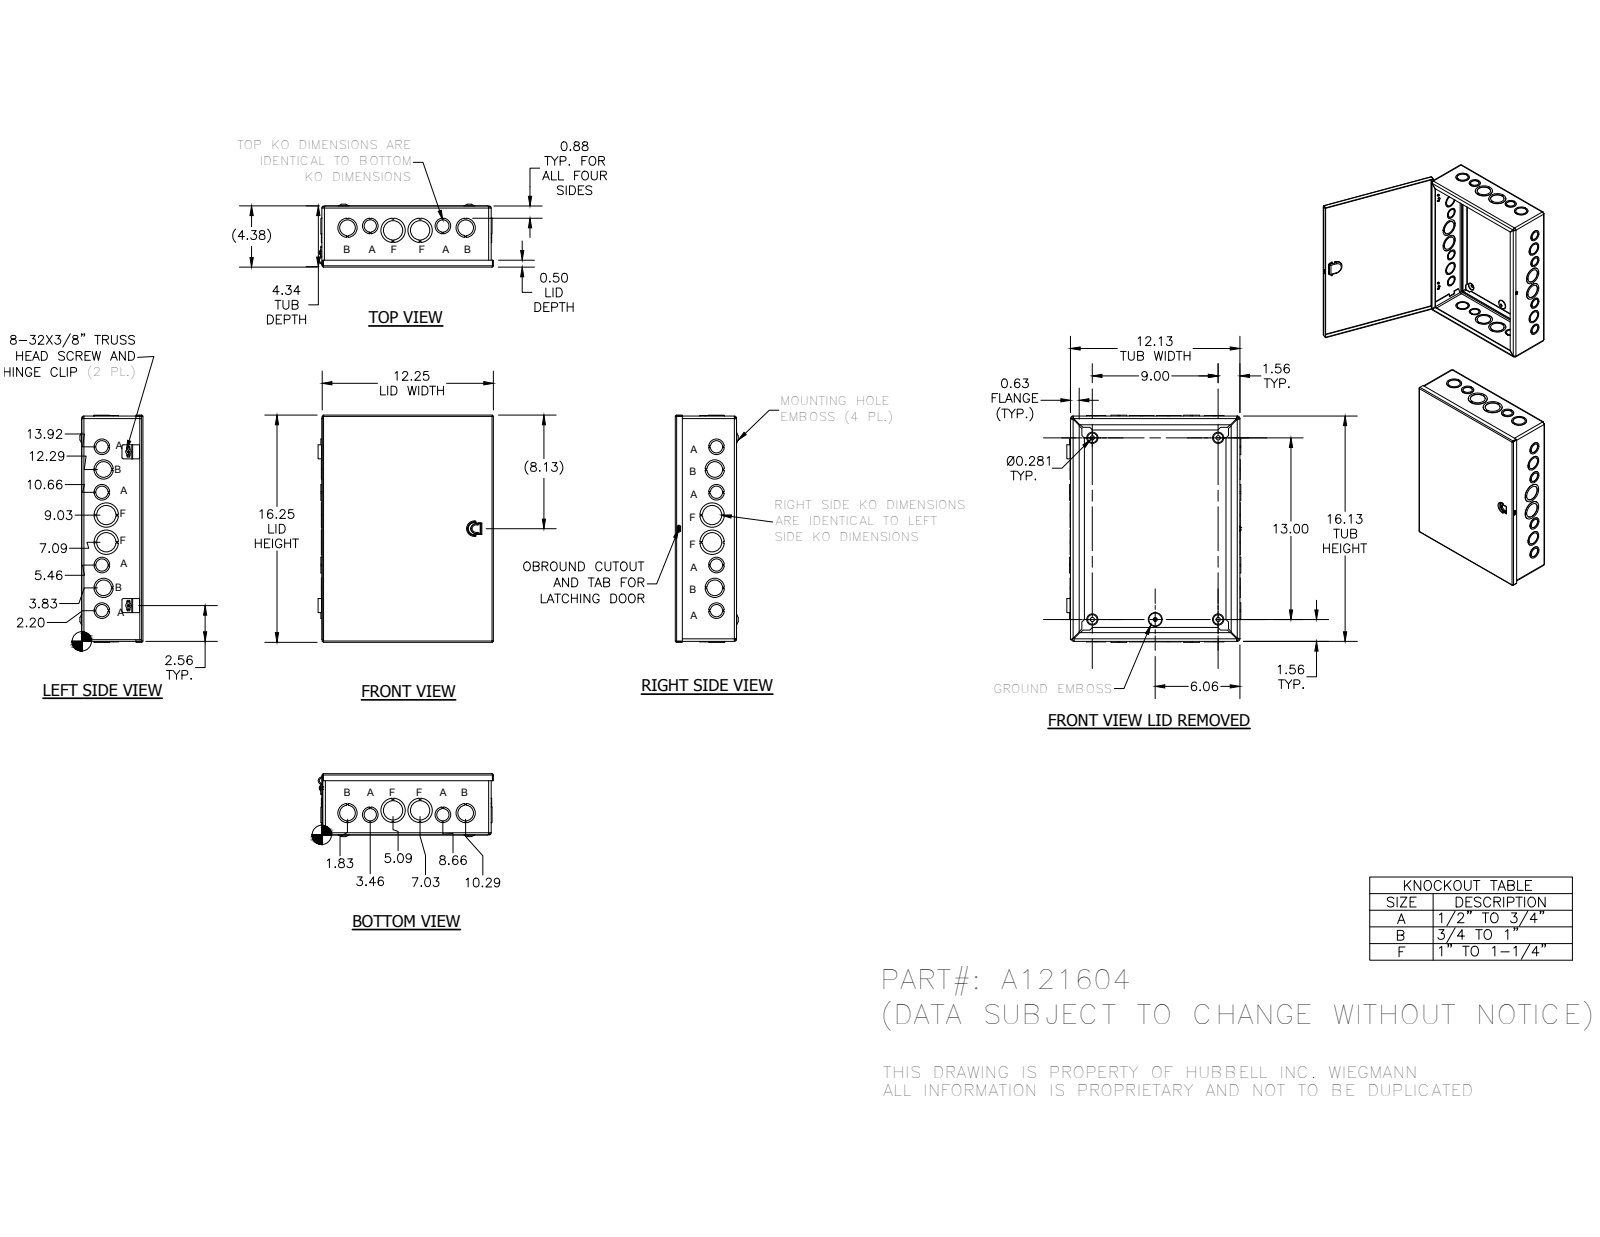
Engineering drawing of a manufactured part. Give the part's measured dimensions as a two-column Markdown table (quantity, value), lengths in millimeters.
| quantity | value |
| --- | --- |
| part name | A1216BA; A121604WRA; 31816; 372177 (+3 more) |
| STEP written by | Autodesk Inventor 2014 (AUTOMOTIVE_DESIGN) |
| units | millimeters |
| bodies | 31 solids, 1279 faces (846 planar, 275 cylindrical, 158 other) |
| overall size | 417.49 × 320.97 × 114.39 |
| round holes (diameter × count) | 28.57 × 10, 34.92 × 8, 22.22 × 6, 7.62 × 4, 44.45 × 4, 3.56 × 2, 4.19 × 1 |
| round bosses / shafts (diameter × count) | 9.75 × 2, 4.17 × 2, 5.8 × 1 |
| partial cylindrical surfaces (radius × count) | 3.17 × 15, 0.79 × 10, 1.59 × 9, 2.38 × 8, 4.75 × 8, 1.4 × 4, 1.57 × 4, 1.78 × 4 |
| main face-to-face distances | 1.58, 1.57, 109.63, 108.05, 1.59, 109.64, 111.22, 408, 307.98, 306.4 |
| hole center spacings | 41.52, 42.15, 82.94, 91.03, 132.17, 173.51, 214.88, 49.26 |
